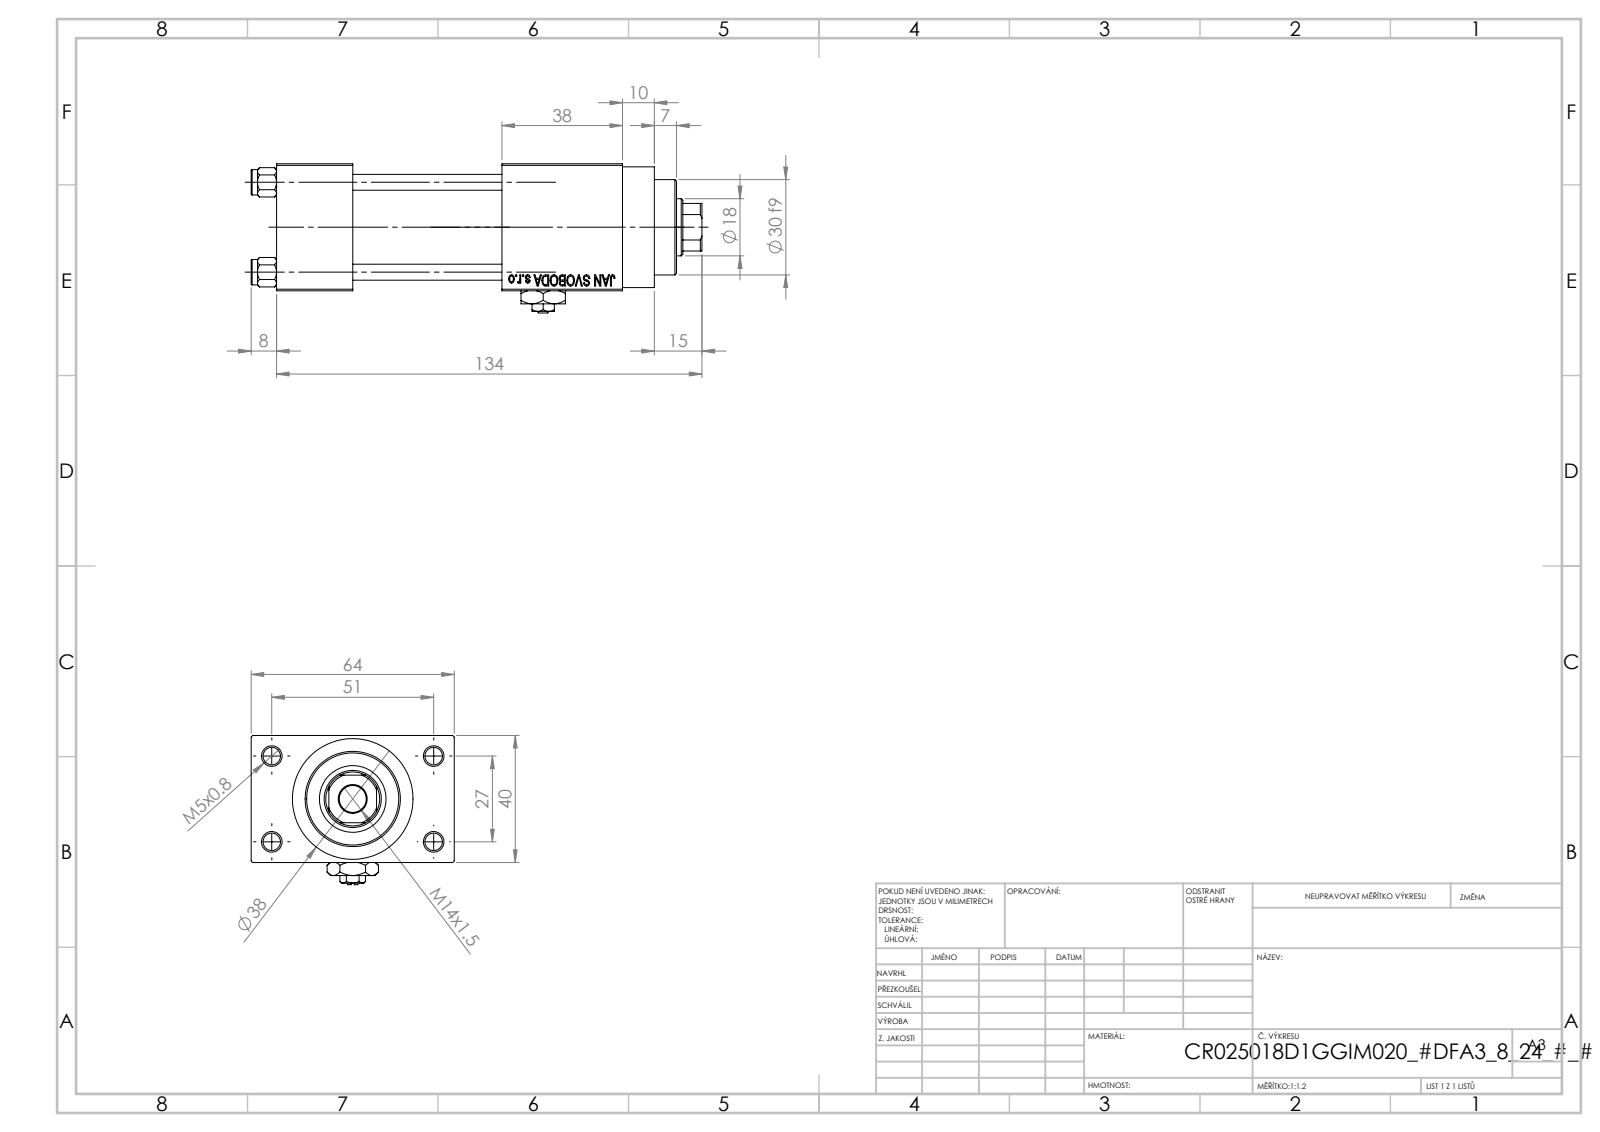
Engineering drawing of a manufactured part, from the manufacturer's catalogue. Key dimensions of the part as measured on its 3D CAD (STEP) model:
Part name (STEP PRODUCT): V215CR_D_Body; NUT_M5_D; V215CR_D_TYCINKA; Zatka_pro_OIL_PORT (+2 more)
STEP written by: SolidWorks 2019 (CONFIG_CONTROL_DESIGN)
Units: millimetres
Bodies: 12 solids, 1147 faces (518 planar, 91 cylindrical, 538 other)
Overall size (bounding box): 142 × 64 × 47
Volume: 180 837 mm³ · Surface area: 64 776 mm²
Round holes (diameter × count): ⌀5 ×4, ⌀5.5 ×4, ⌀20 ×3, ⌀7 ×2, ⌀13.16 ×2, ⌀8.5 ×1, ⌀18 ×1, ⌀21 ×1, ⌀25 ×1, ⌀30 ×1
Round bosses / shafts (diameter × count): ⌀8 ×4, ⌀38 ×1, ⌀31 ×1
Partial cylindrical surfaces — rounded edges, fillets, slot ends (radius × count): R8.5 ×1
Main face-to-face distances: 40, 12, 52, 47, 24, 71, 64, 38, 85, 109
Hole centre spacings: 11.37, 20.01, 28.3, 28.85, 29.89, 39.66, 48.34, 27
